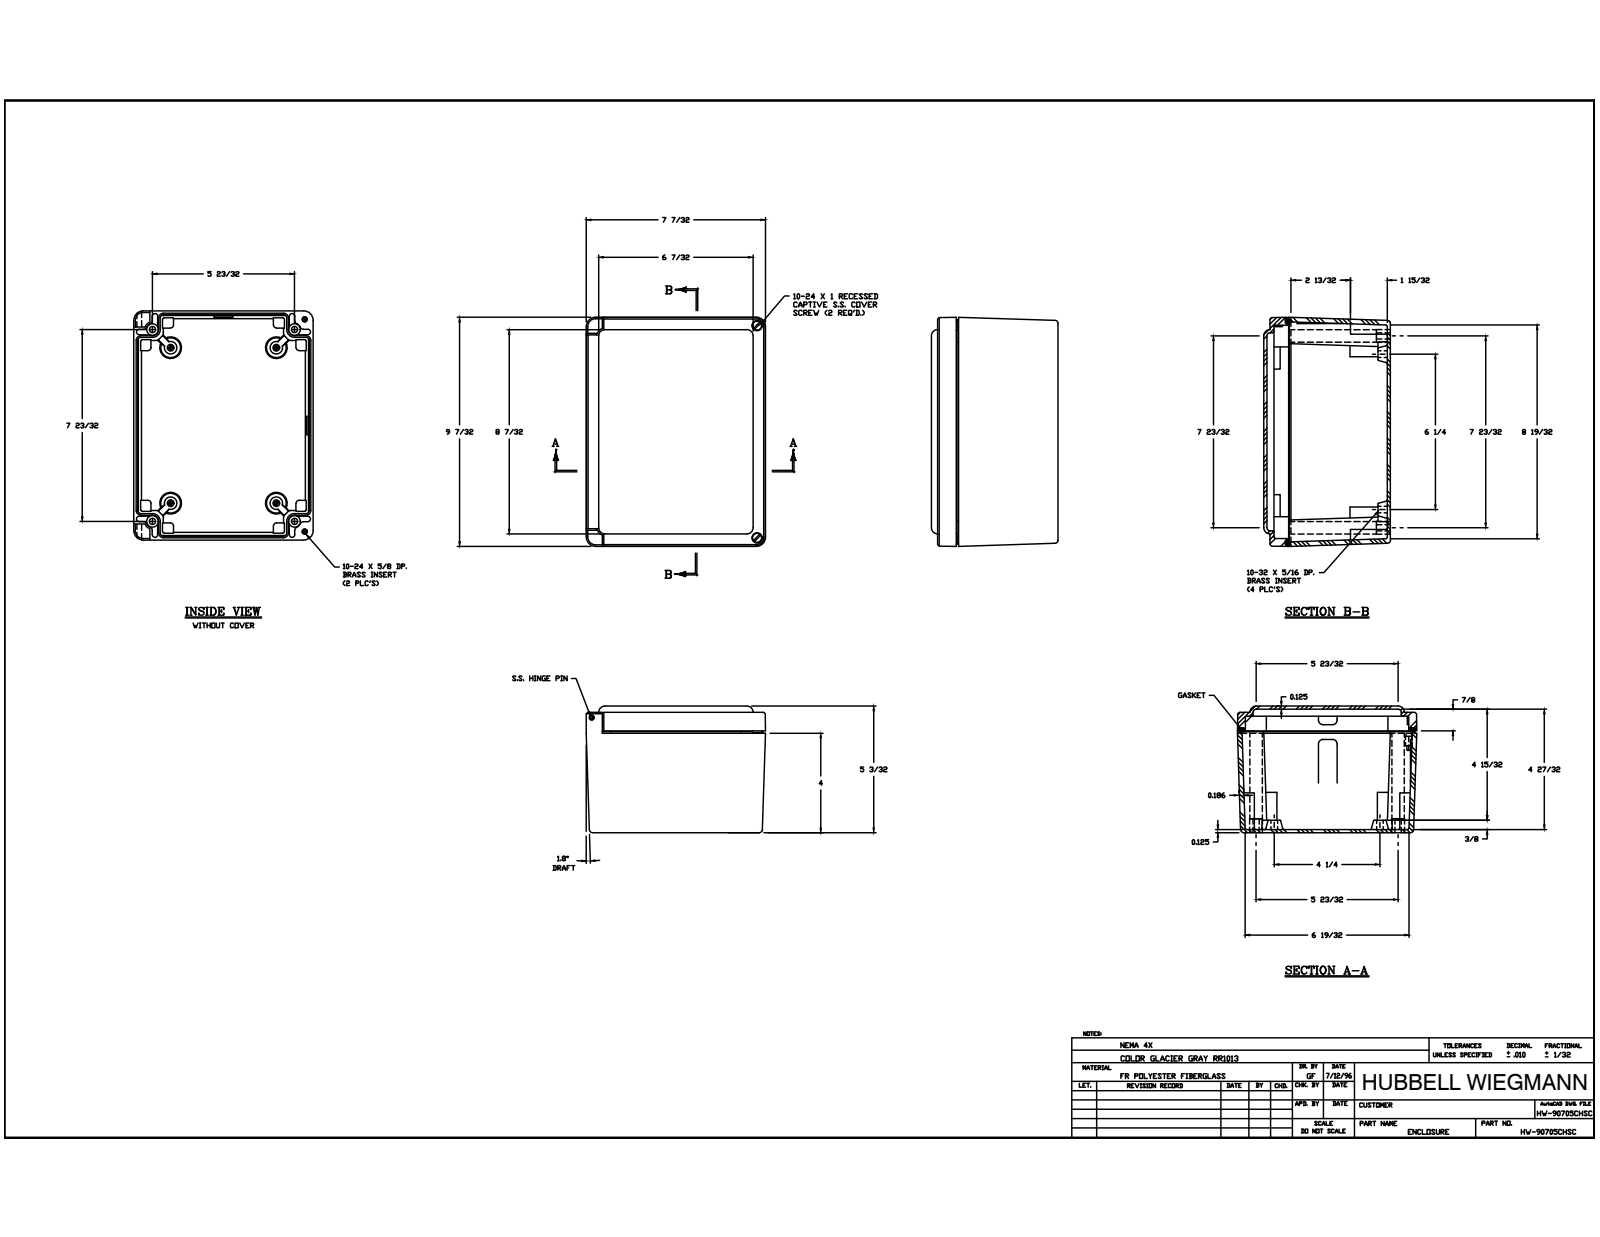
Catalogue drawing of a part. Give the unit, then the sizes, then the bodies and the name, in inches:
Units: inches
Overall size (bounding box): 9.22 × 7.22 × 5.094
Round holes (diameter × count): ⌀0.281 ×6, ⌀0.156 ×4, ⌀0.313 ×4, ⌀0.531 ×4, ⌀0.096 ×2, ⌀0.145 ×2, ⌀0.156 ×2, ⌀0.19 ×2, ⌀0.219 ×2, ⌀0.23 ×2, ⌀0.28 ×2, ⌀0.406 ×2
Round bosses / shafts (diameter × count): ⌀0.375 ×2, ⌀0.364 ×2, ⌀0.234 ×2, ⌀0.191 ×2, ⌀0.095 ×2, ⌀0.371 ×1, ⌀0.178 ×1, ⌀0.088 ×1
Partial cylindrical surfaces — rounded edges, fillets, slot ends (radius × count): R0.031 ×60, R0.125 ×38, R0.063 ×29, R0.01 ×8, R0.059 ×8, R0.188 ×8, R0.25 ×8, R0.375 ×8
Main face-to-face distances: 0.125, 4.969, 0.186, 5.094, 4.844, 0.125, 0.25, 0.75, 4.844, 4.719
Hole centre spacings: 1.039, 5.04, 7.024, 8.583, 8.531, 0.528, 0.572, 0.573
Volume: 57.16 in³ · Surface area: 649.3 in²
Bodies: 23 solids, 1023 faces (397 planar, 294 cylindrical, 332 other)
Part name (STEP PRODUCT): WP907HWBOX; 0.3125-18 X 0.563 DP BRASS INSERT; 10-32 X0.3125 DP BRASS INSERT; 10-24 X 0.625 DP BRASS INSERT (+8 more)
STEP written by: Autodesk Inventor 2014 (AUTOMOTIVE_DESIGN)
